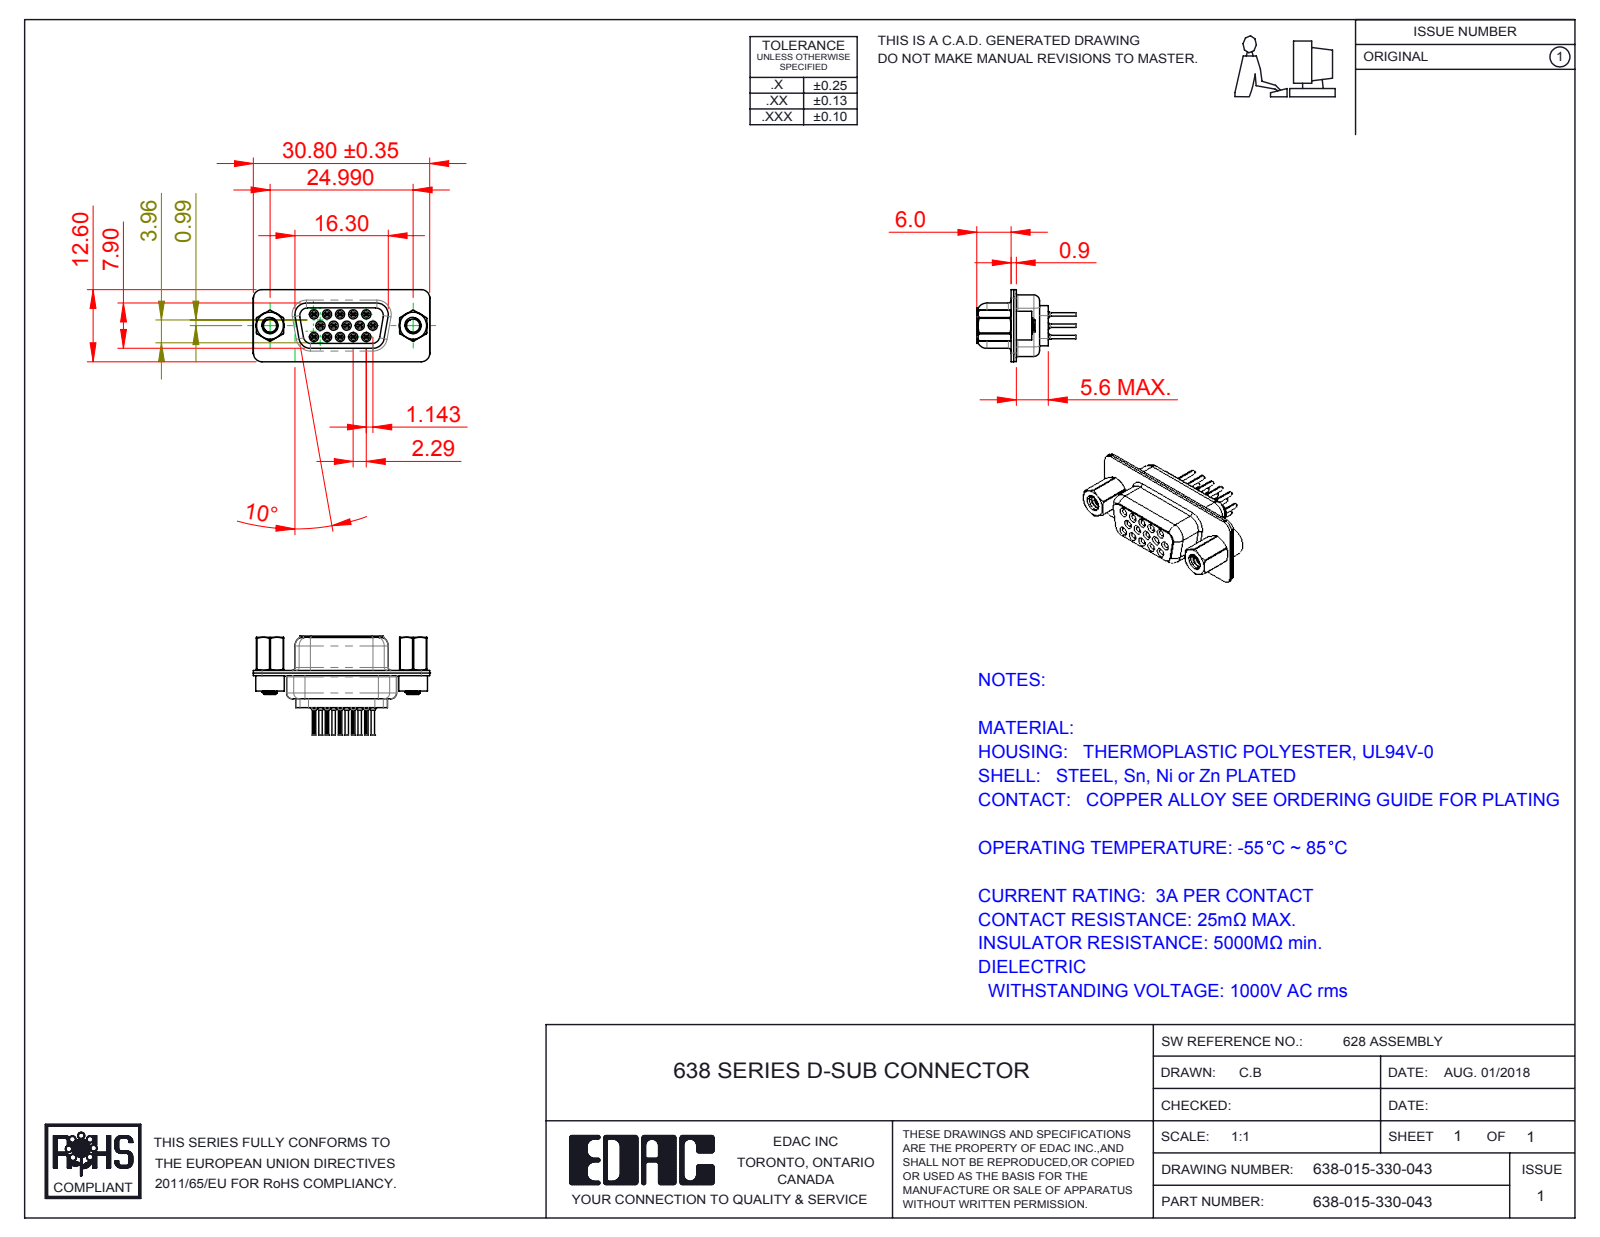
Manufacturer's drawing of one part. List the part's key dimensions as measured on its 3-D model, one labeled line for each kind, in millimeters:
Part name (STEP PRODUCT): 638 Housing_15 Contacts; 638 Shell Rear_15 Contacts; 638 4-40 Hex Standoff; 638 Contact Row 1_30L (+5 more)
STEP written by: SolidWorks 2016 (CONFIG_CONTROL_DESIGN)
Units: millimetres
Bodies: 22 solids, 2310 faces (554 planar, 704 cylindrical, 1052 other)
Overall size (bounding box): 30.81 × 17.3 × 12.6
Volume: 1 789 mm³ · Surface area: 6 081 mm²
Round holes (diameter × count): ⌀0.2 ×15, ⌀0.8 ×15, ⌀1 ×15, ⌀1.1 ×15, ⌀1.6 ×15, ⌀1.7 ×15, ⌀1.8 ×15, ⌀2 ×2, ⌀2.26 ×2, ⌀2.29 ×2, ⌀4 ×2, ⌀4.05 ×2
Round bosses / shafts (diameter × count): ⌀2 ×15, ⌀1.5 ×15, ⌀1.2 ×15, ⌀0.6 ×15, ⌀5 ×2, ⌀4.95 ×2, ⌀4.8 ×2, ⌀2.79 ×2
Partial cylindrical surfaces — rounded edges, fillets, slot ends (radius × count): R0.1 ×30, R1.5 ×20, R2 ×12, R0.28 ×10, R1.55 ×8, R1.35 ×5, R0.25 ×4, R0.5 ×4
Main face-to-face distances: 0.45, 0.9, 0.4, 1.43, 8.88, 6.6, 1.4, 2.28, 6.2, 0.85
Hole centre spacings: 3.96, 2.28, 4.57, 2.29, 6.05, 6.04, 6.86, 7.92
